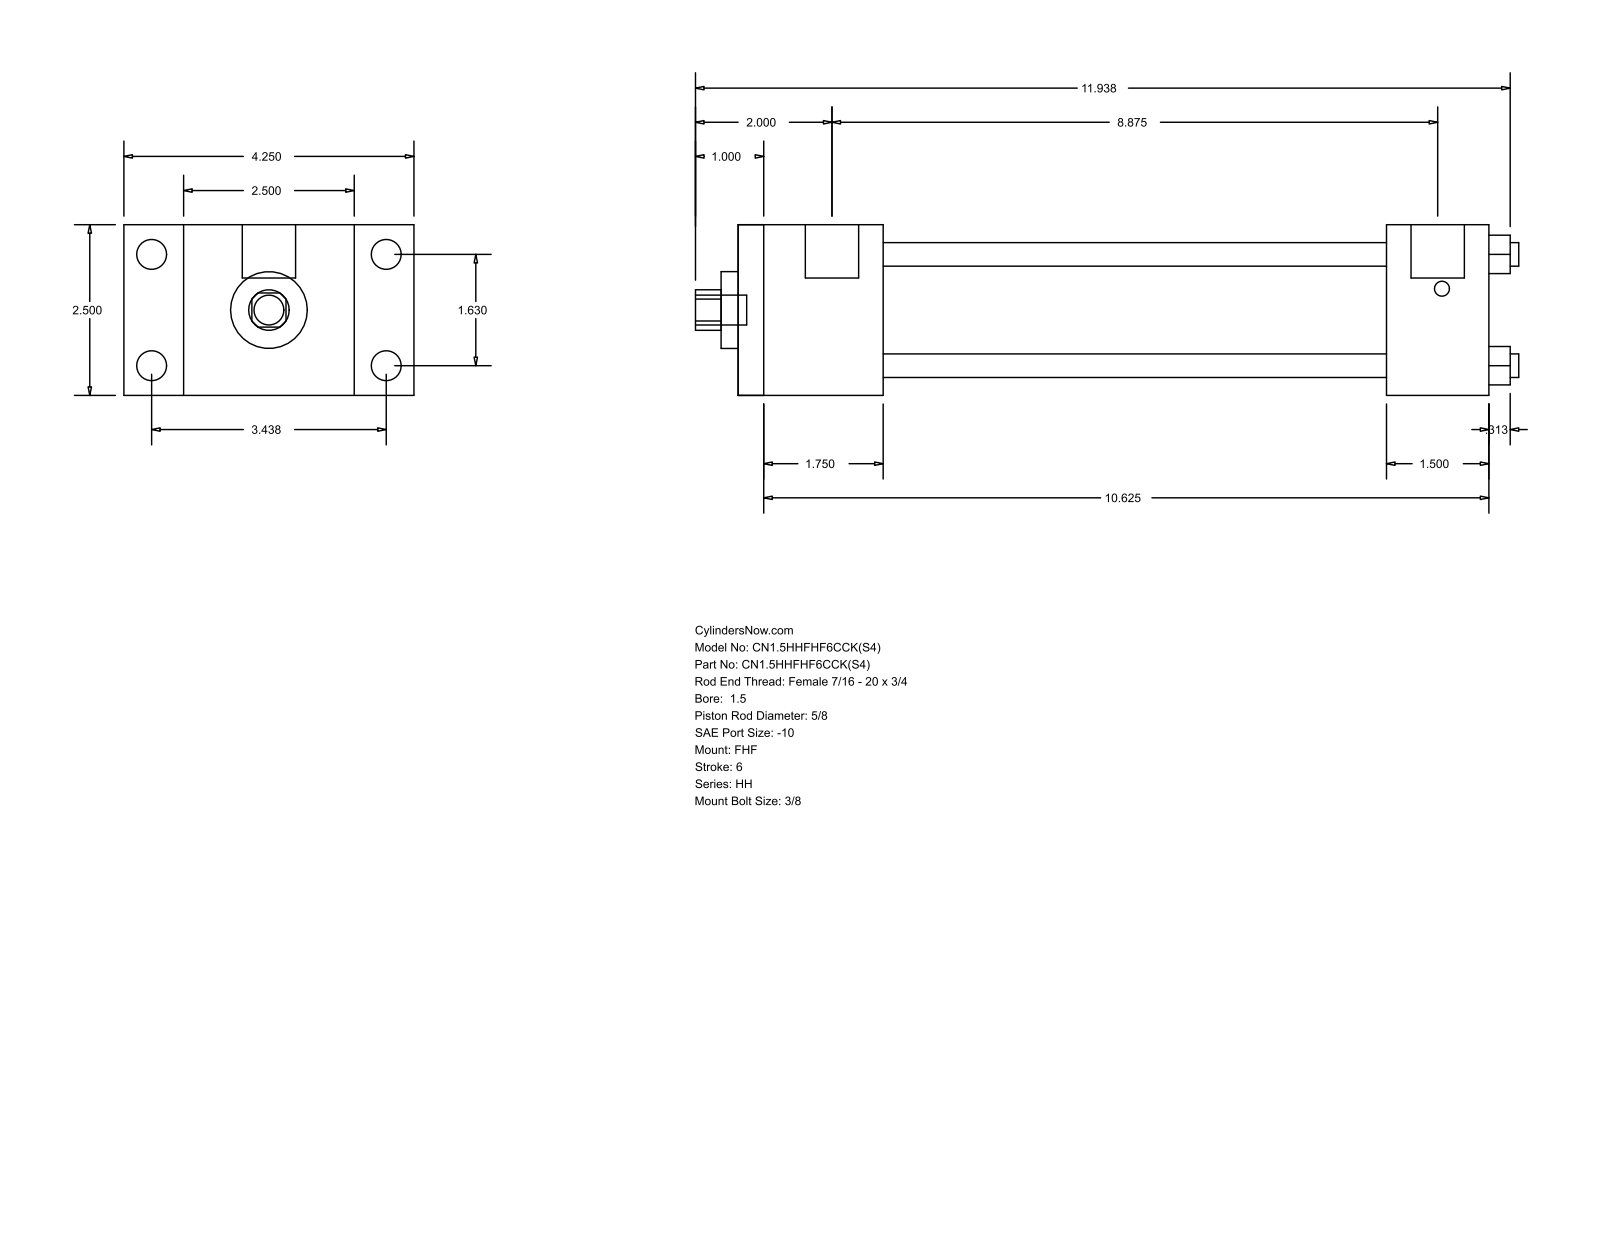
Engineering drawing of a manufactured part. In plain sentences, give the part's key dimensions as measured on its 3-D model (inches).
The part is named "HH_FHF__0150_0.625". Its 3-D file was written by "GSSL Pune (CONFIG_CONTROL_DESIGN)". It is 0 solids with 88 faces: 60 planar, 28 cylindrical and 0 other. Overall it measures 12.063 by 4.25 by 2.5 inches. Round holes: 4 of diameter 0.345, 1 of diameter 0.625, 1 of diameter 1.125, 1 of diameter 1.75. Round bosses or shafts: 4 of diameter 0.438, 4 of diameter 0.219, 2 of diameter 0.781, 1 of diameter 0.437. Partial cylindrical surfaces (rounded edges, fillets, slot ends): 1 of radius 0.297. The main face-to-face distances are 2.5, 0.875, 3.375, 2.125, 4.25, 11, 8.875, 9.5, 7.375, 1.5. The hole center spacings are 1.152, 1.63, 2.305.
